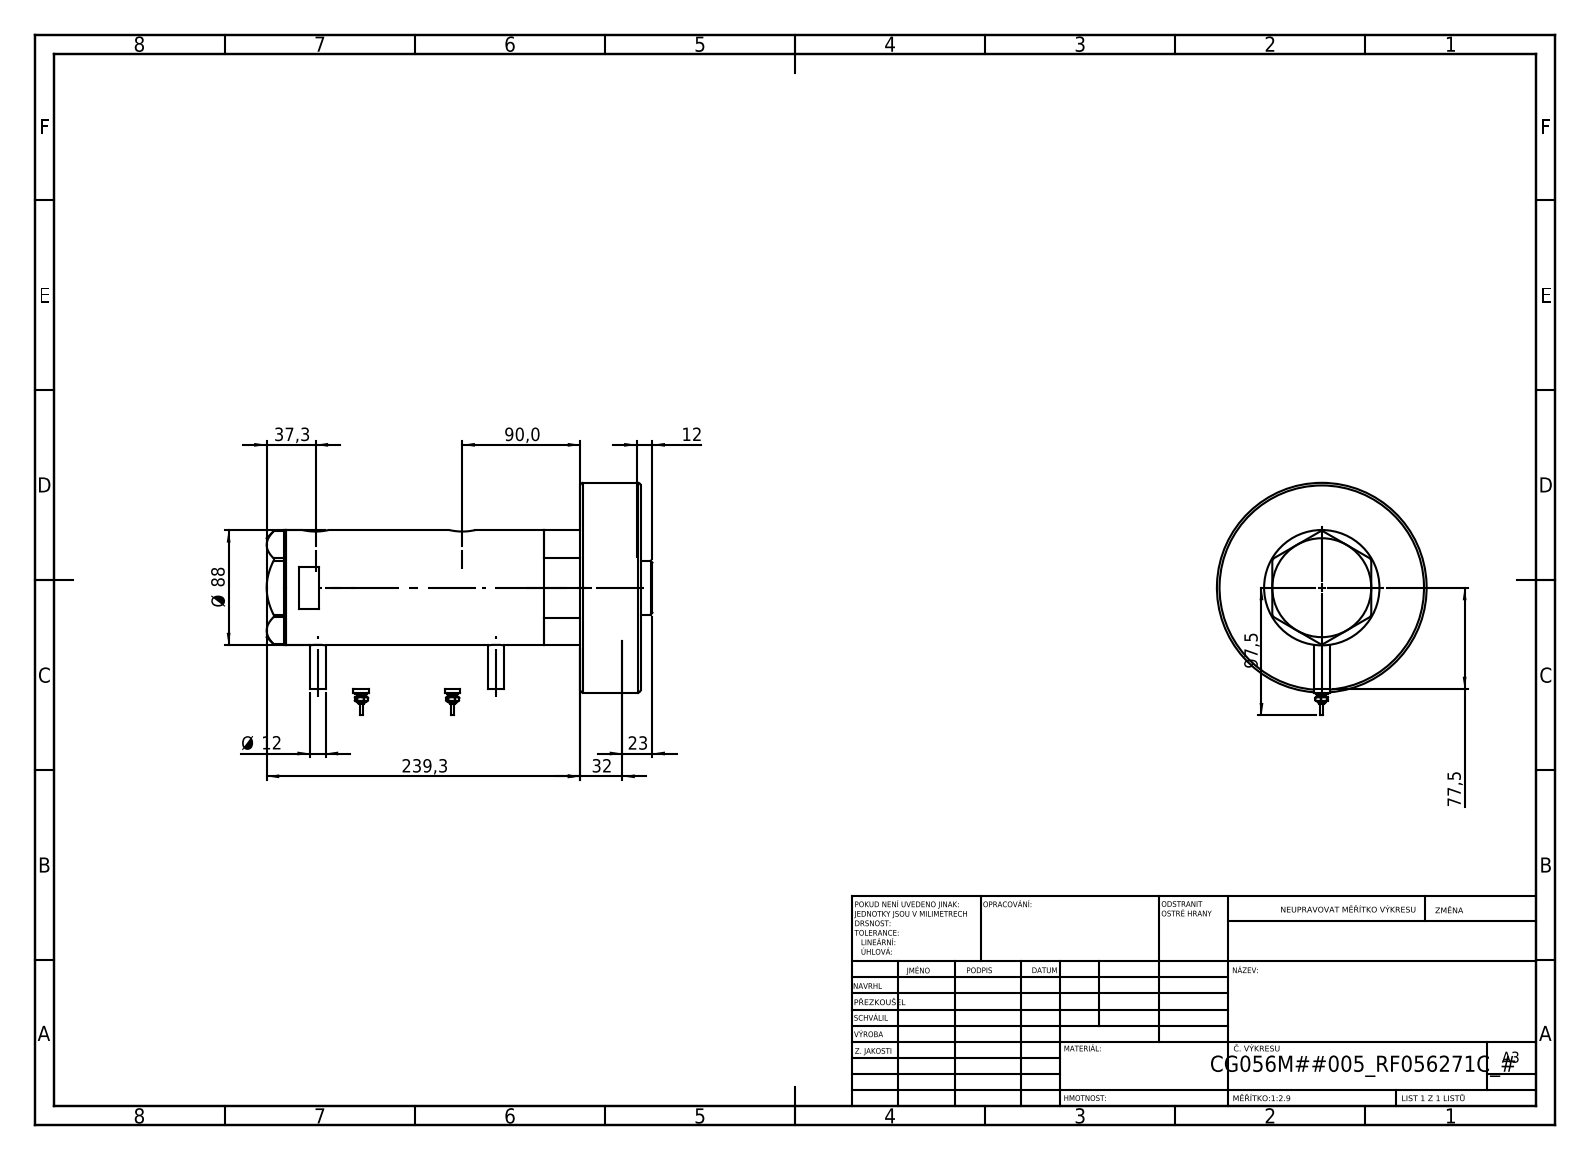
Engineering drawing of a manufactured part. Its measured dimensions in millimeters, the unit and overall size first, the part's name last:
Units: millimetres
Overall size (bounding box): 294.3 × 177.5 × 160
Round holes (diameter × count): ⌀12.5 ×2, ⌀13.16 ×2, ⌀20 ×2, ⌀14.5 ×1, ⌀42 ×1, ⌀43.5 ×1, ⌀56 ×1, ⌀60 ×1, ⌀75 ×1, ⌀80 ×1
Round bosses / shafts (diameter × count): ⌀12 ×4, ⌀9 ×2, ⌀7 ×2, ⌀4.5 ×2, ⌀2.5 ×2, ⌀160 ×1, ⌀88 ×1, ⌀73 ×1
Main face-to-face distances: 46, 224.3, 270.3, 134.4, 89.9, 135.9, 244.3, 26, 108.4, 198.3
Hole centre spacings: 1.7, 25.8, 110.3, 112, 136.1, 137.8
Volume: 2 310 000 mm³ · Surface area: 291 039 mm²
Bodies: 7 solids, 223 faces (82 planar, 73 cylindrical, 68 other)
Part name (STEP PRODUCT): V270CG_FRONT; Switch; V270CG_VC; V270CG_BACK (+2 more)
STEP written by: SolidWorks 2019 (CONFIG_CONTROL_DESIGN)
